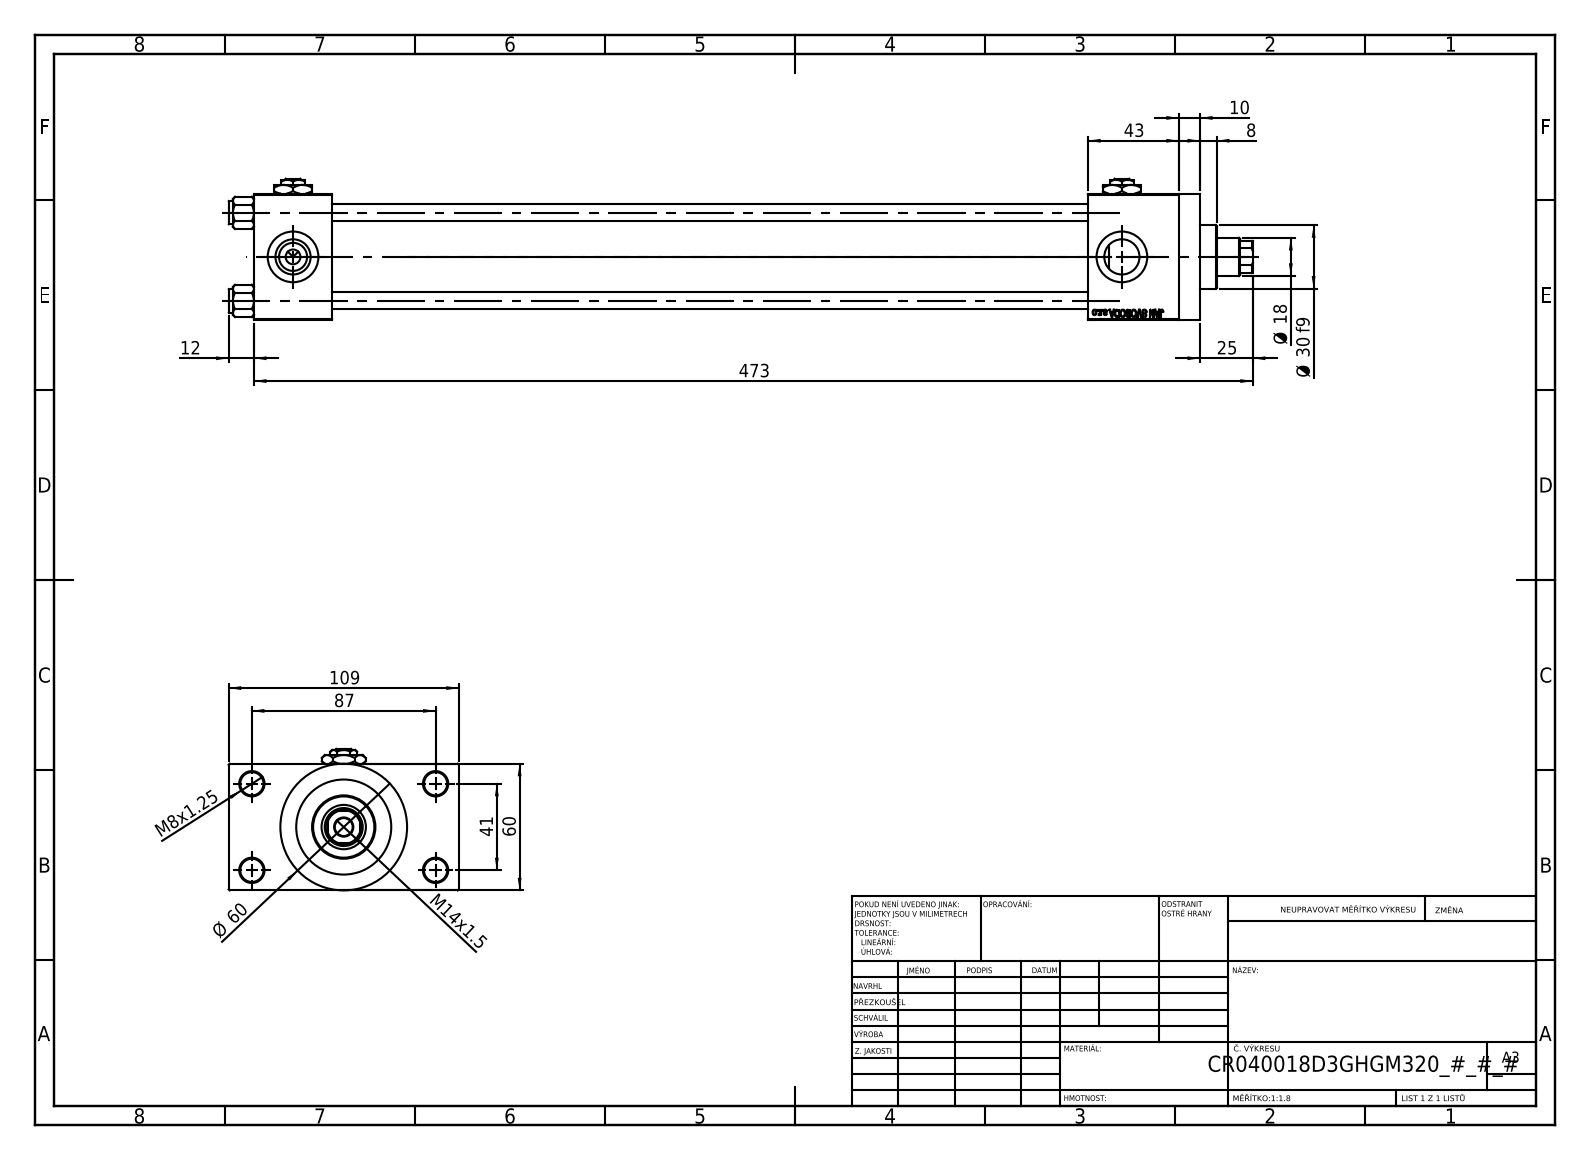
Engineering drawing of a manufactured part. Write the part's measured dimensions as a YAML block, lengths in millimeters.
part_name: "V215CR_D_TYCINKA; V215_VC_A; V215CR_VCP_D; V215CR_D_Body (+2 more)"
step_written_by: "SolidWorks 2019 (CONFIG_CONTROL_DESIGN)"
units: millimeters
bodies: {solids: 13, faces: 1205, planar: 546, cylindrical: 99, other: 560}
overall_size: [485, 109, 67]
volume: 768576
surface_area: 253369
round_holes:
  - {diameter: 8, count: 4}
  - {diameter: 11, count: 4}
  - {diameter: 16.66, count: 4}
  - {diameter: 24, count: 4}
  - {diameter: 7, count: 3}
  - {diameter: 8.5, count: 1}
  - {diameter: 18, count: 1}
  - {diameter: 21, count: 1}
  - {diameter: 31, count: 1}
  - {diameter: 40, count: 1}
  - {diameter: 45, count: 1}
round_bosses_or_shafts:
  - {diameter: 11, count: 4}
  - {diameter: 60, count: 1}
  - {diameter: 46, count: 1}
  - {diameter: 30, count: 1}
partial_cylinders:
  - {radius: 8.5, count: 1}
face_to_face_distances: [60, 358, 24.5, 84.5, 37, 395, 43, 438, 401, 10]
hole_center_spacings: [22.65, 29.49, 41.7, 47.15, 48.09, 64.35, 76.49, 41]
